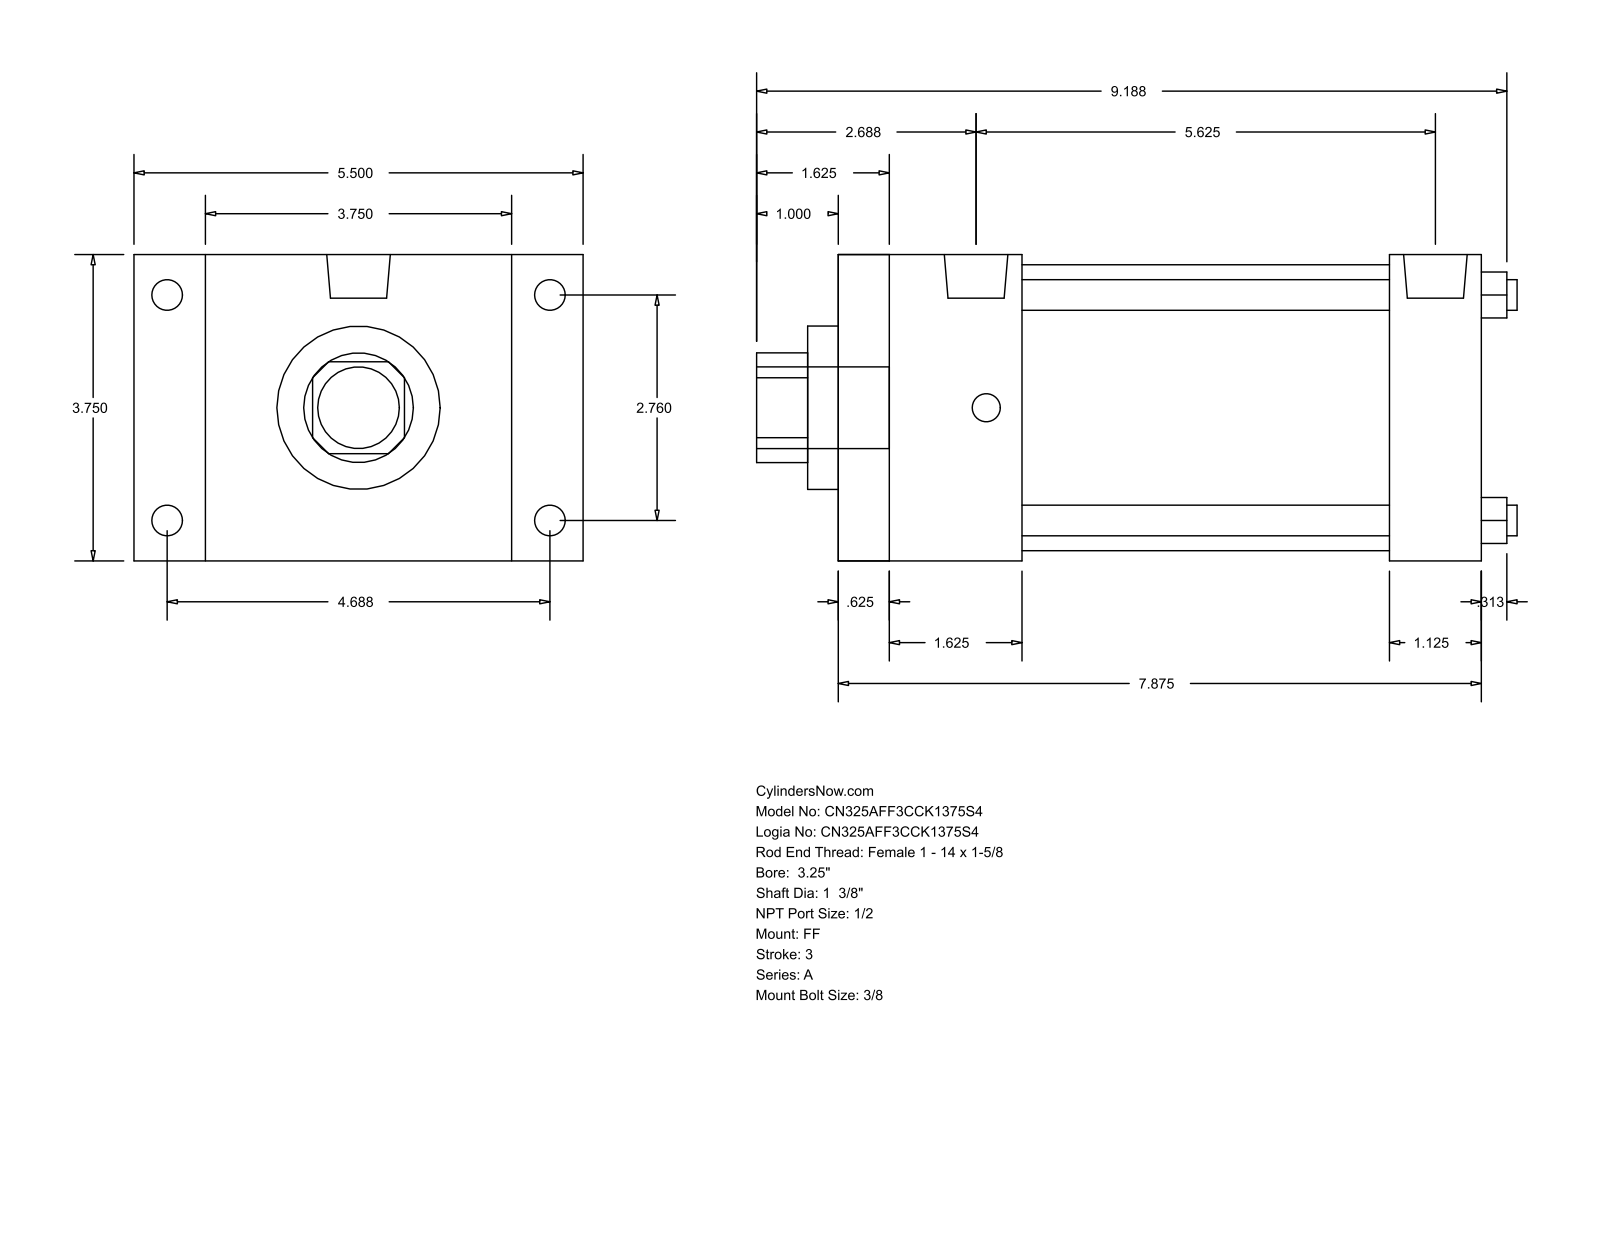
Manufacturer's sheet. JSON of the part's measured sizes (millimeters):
{"part_name": "A_FF__0325_1.375", "step_written_by": "GSSL Pune (CONFIG_CONTROL_DESIGN)", "units": "millimeters", "bodies": {"solids": 0, "faces": 92, "planar": 64, "cylindrical": 28, "other": 0}, "overall_size": [236.54, 139.7, 95.25], "round_holes": [[9.53, 4], [34.92, 1], [50.8, 1], [88.9, 1]], "round_bosses_or_shafts": [[9.53, 4], [8.73, 4], [19.77, 2], [25.4, 1]], "partial_cylinders_radius": [[17.06, 1]], "face_to_face_distances": [95.24, 200.03, 15.87, 184.16, 28.58, 22.23, 117.47, 57.15, 171.45, 41.28], "hole_center_spacings": [49.57, 70.1, 99.14]}
